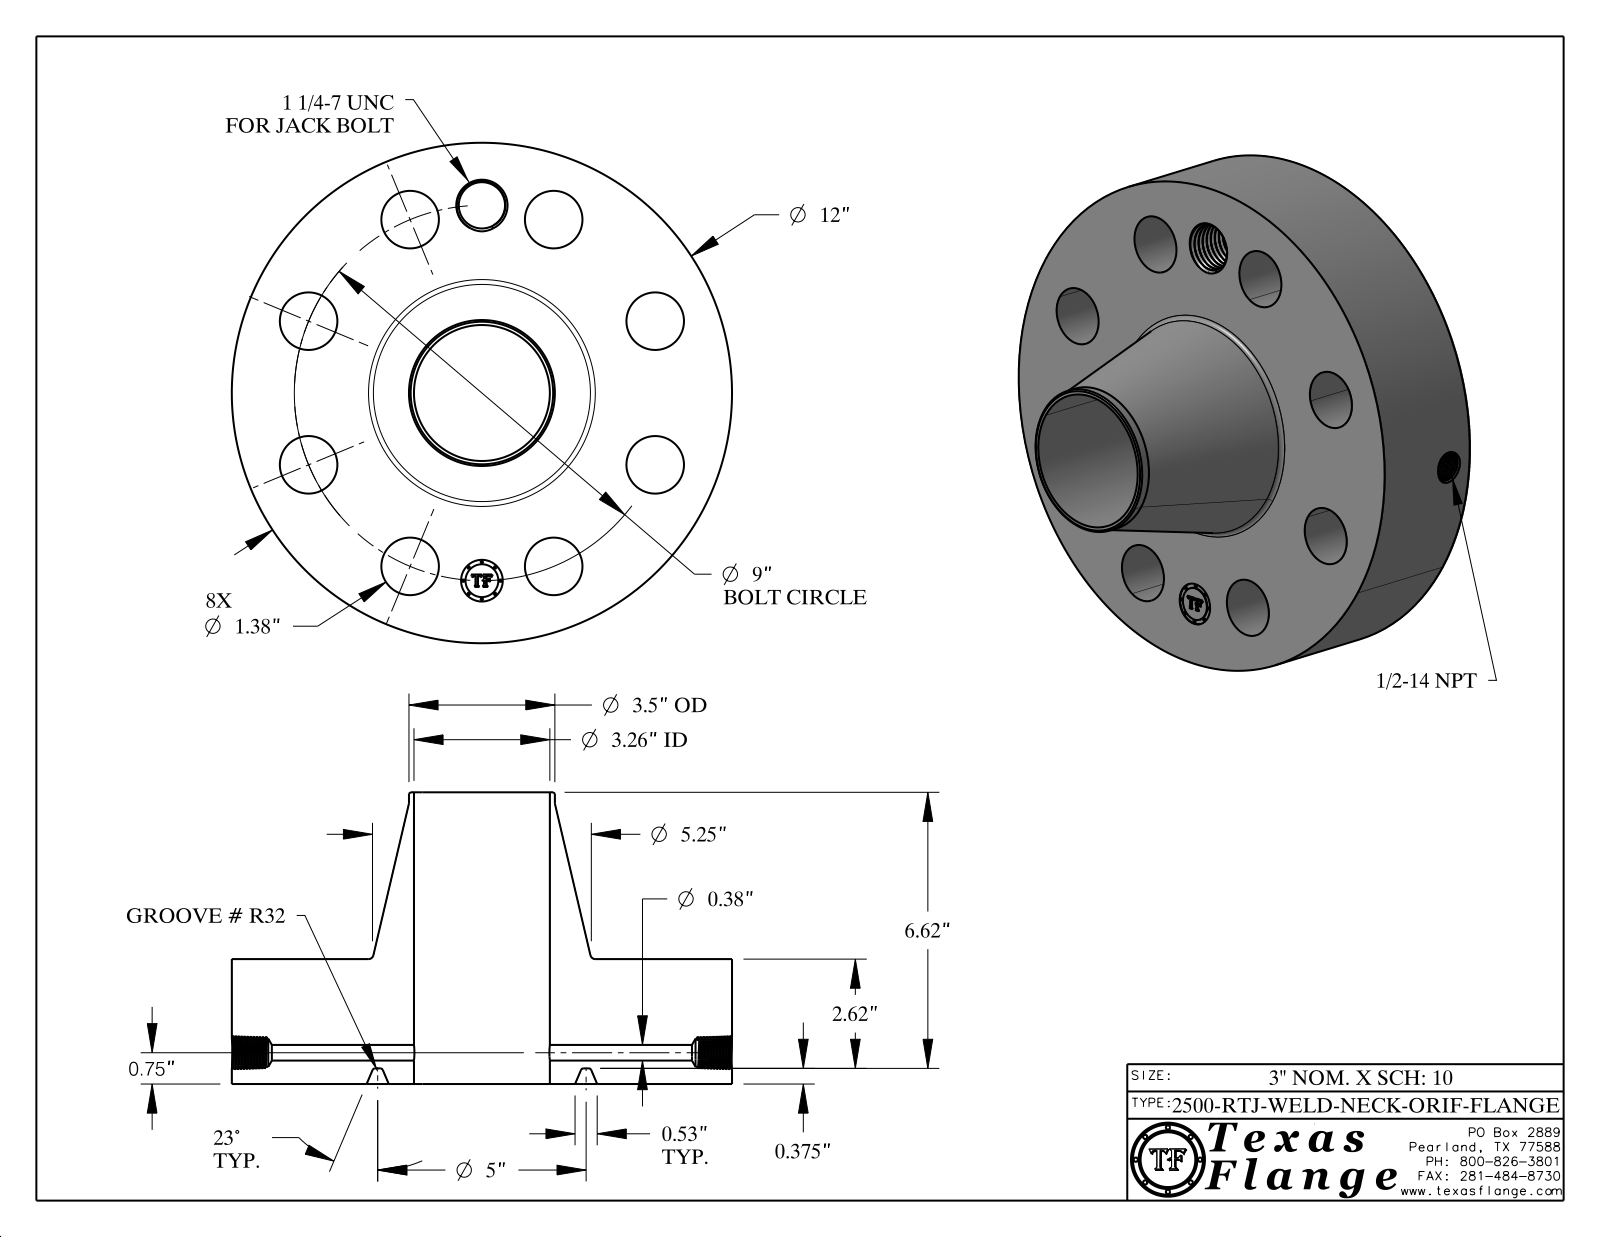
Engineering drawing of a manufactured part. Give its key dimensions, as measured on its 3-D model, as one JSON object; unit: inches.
{"part_name": "2500-RTJ-WELD-NECK", "step_written_by": "CATIA V5 STEP AP214 (AUTOMOTIVE_DESIGN)", "units": "inches", "bodies": {"solids": 1, "faces": 813, "planar": 370, "cylindrical": 103, "other": 340}, "overall_size": [12, 12, 6.995], "volume_in3": 297, "surface_area_in2": 552.5, "round_holes": [[1.38, 8], [0.375, 1], [0.672, 1], [1, 1], [1.109, 1], [3.26, 1]], "round_bosses_or_shafts": [[0.061, 8], [12, 1], [3.5, 1], [0.788, 1]], "face_to_face_distances": [2.995, 0.375, 2.62, 6.995, 6.62, 4, 2.98, 2.605, 0.015, 4.015], "hole_center_spacings": [4.5, 3.444, 6.364, 8.315, 9, 1.756, 5, 7.483]}
